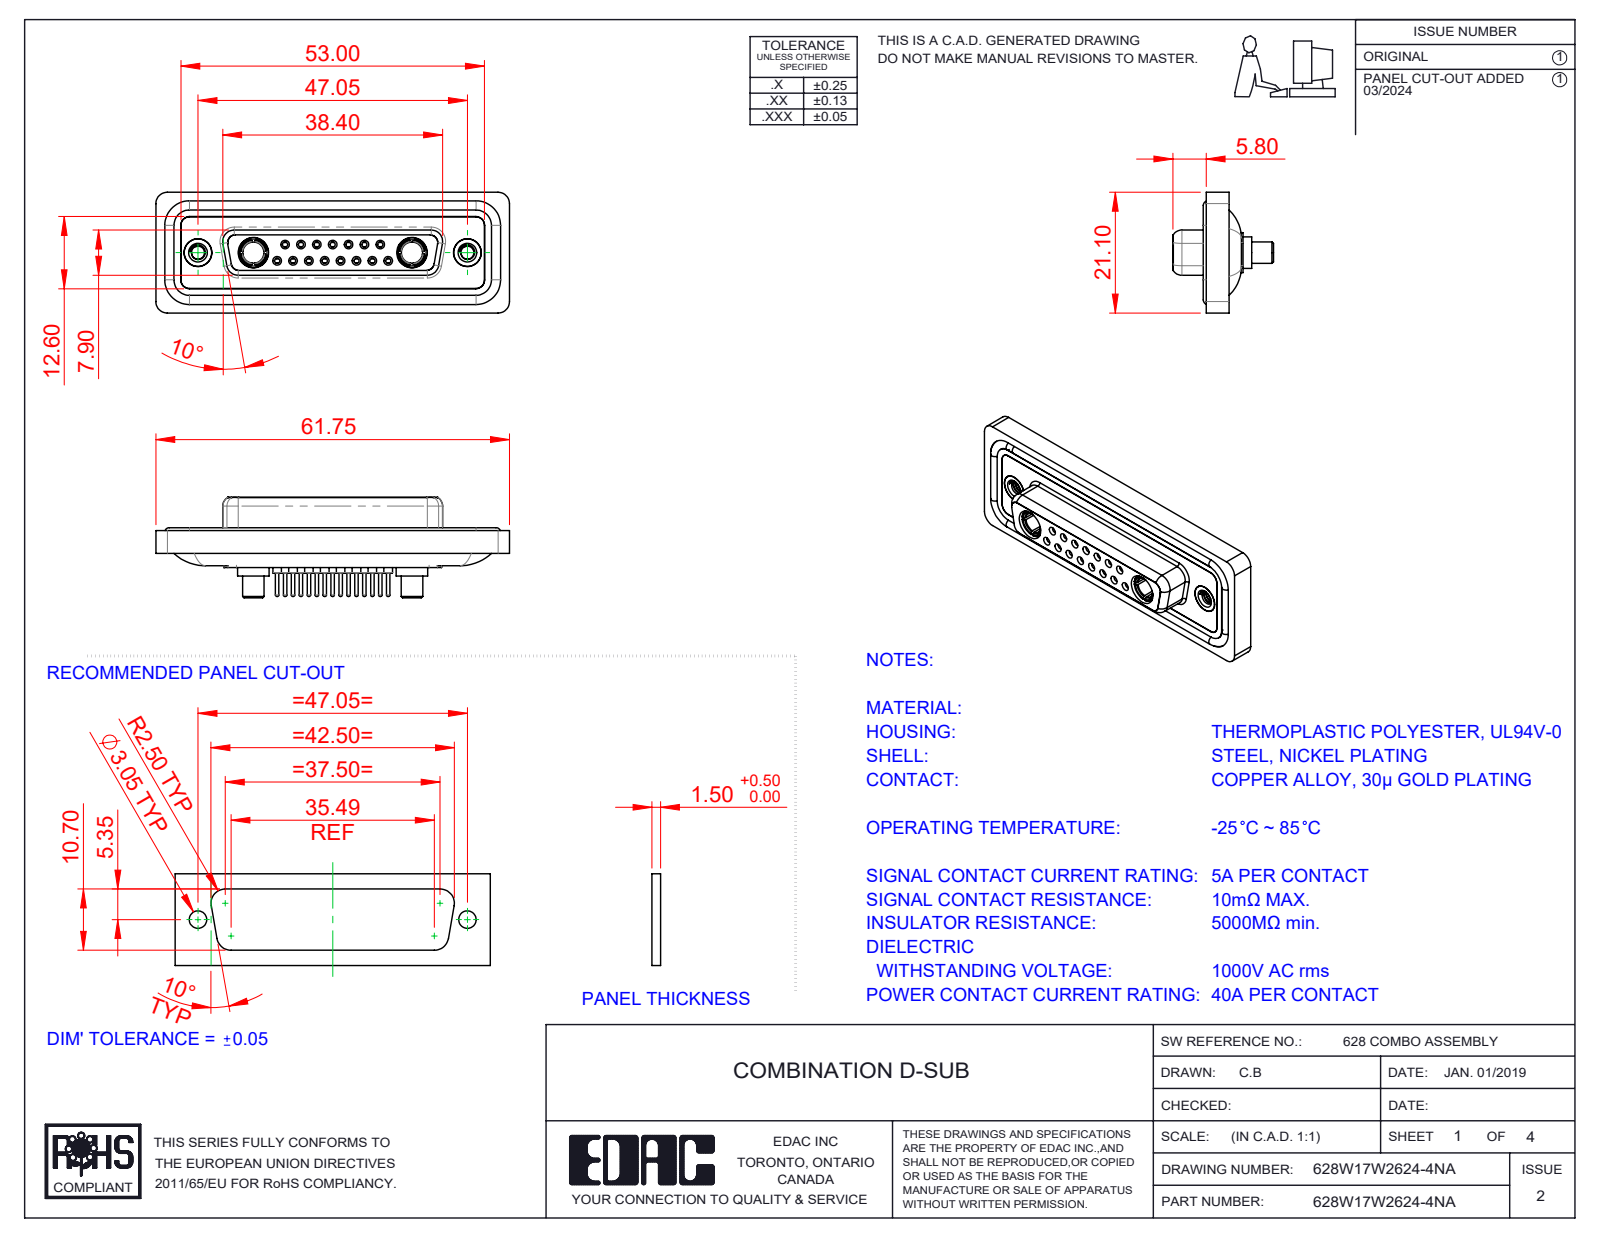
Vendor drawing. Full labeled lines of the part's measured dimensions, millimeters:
Part name (STEP PRODUCT): 628Combo Shell Rear_25 Contacts; 628W17W2624-4NA; 628Combo Housing_17W2; 628Combo Waterproof Housing_25 Contacts (+5 more)
STEP written by: SolidWorks 2023 (CONFIG_CONTROL_DESIGN)
Units: millimetres
Bodies: 26 solids, 1357 faces (388 planar, 521 cylindrical, 448 other)
Overall size (bounding box): 61.75 × 21.1 × 17.55
Volume: 8 363 mm³ · Surface area: 13 875 mm²
Round holes (diameter × count): ⌀0.9 ×15, ⌀1.1 ×15, ⌀1.5 ×15, ⌀2 ×15, ⌀1.6 ×8, ⌀1.7 ×7, ⌀4.85 ×4, ⌀2.26 ×2, ⌀3.7 ×2, ⌀4 ×2, ⌀4.05 ×2, ⌀5 ×2
Round bosses / shafts (diameter × count): ⌀2.2 ×15, ⌀0.6 ×15, ⌀1.6 ×11, ⌀5.5 ×2, ⌀5.2 ×2, ⌀4.96 ×2, ⌀4.95 ×2, ⌀4.8 ×2
Partial cylindrical surfaces — rounded edges, fillets, slot ends (radius × count): R1.5 ×22, R2 ×18, R1.35 ×8, R1.6 ×8, R0.25 ×4, R0.5 ×4, R0.6 ×4, R0.65 ×4
Main face-to-face distances: 0.4, 1.8, 7.45, 5.65, 6.6, 0.5, 7.05, 1.6, 2.9, 1.1
Hole centre spacings: 3.16, 2.77, 8.31, 5.54, 5.03, 5.04, 7.49, 11.08
